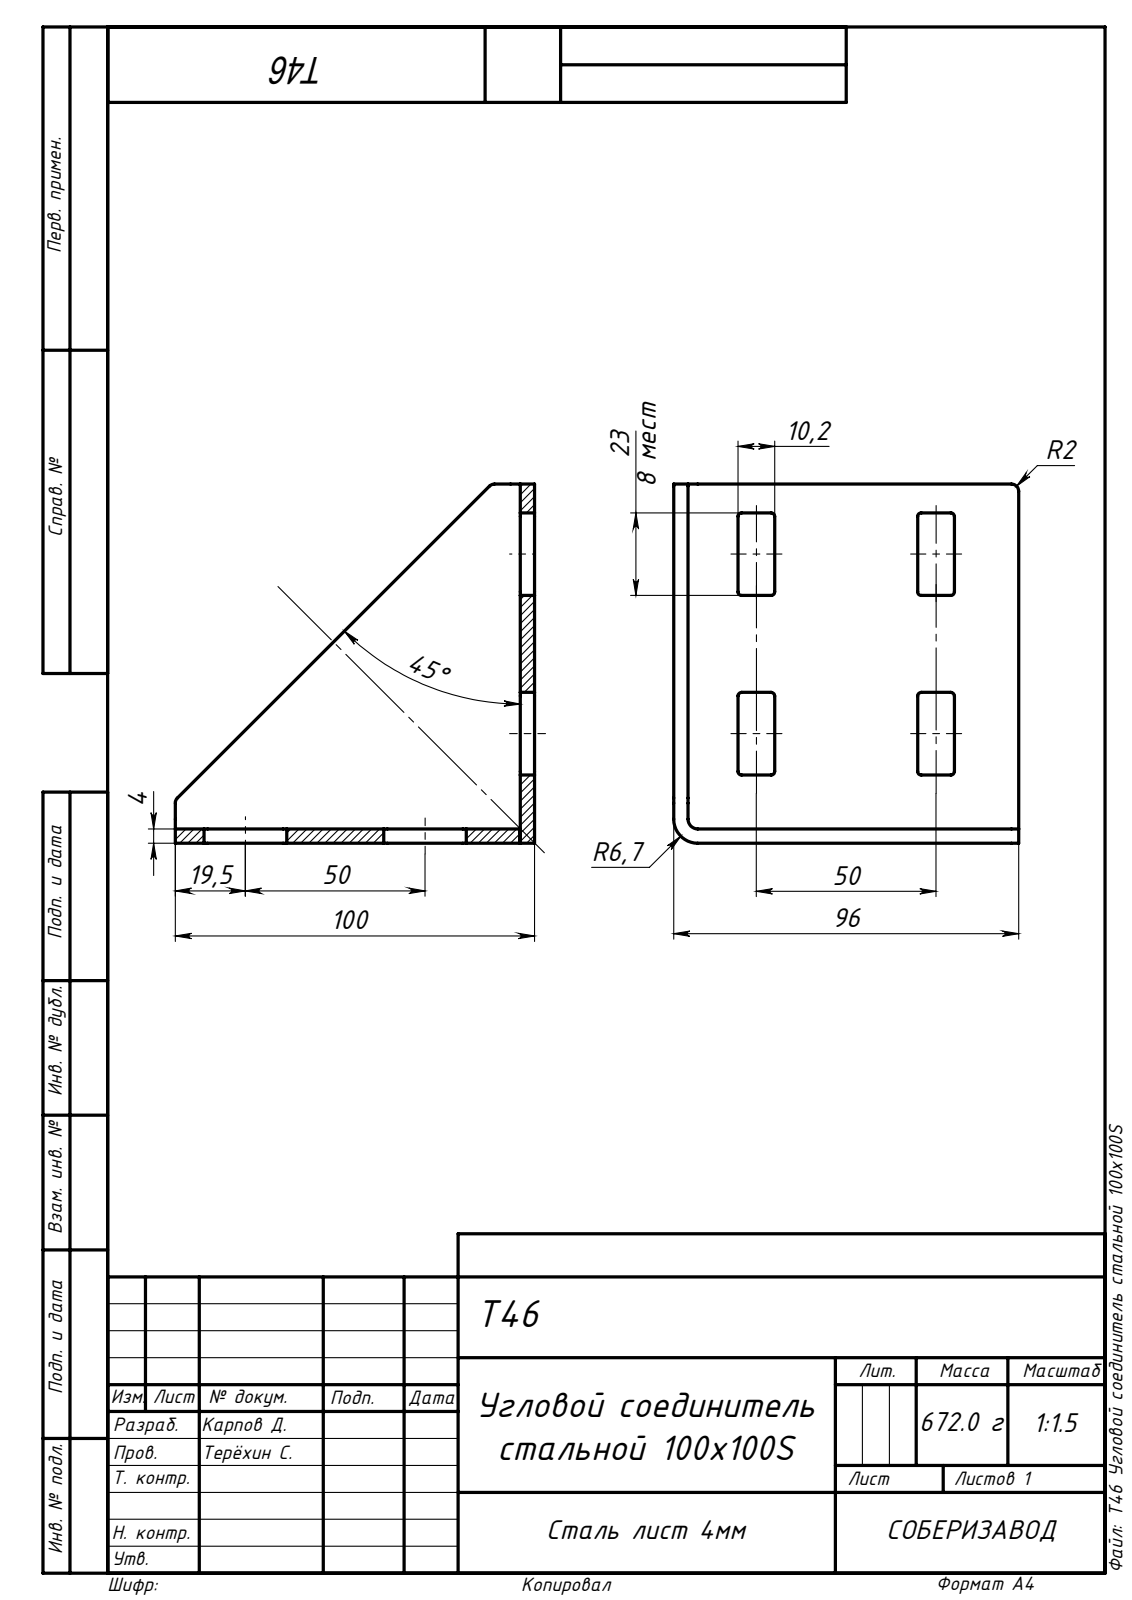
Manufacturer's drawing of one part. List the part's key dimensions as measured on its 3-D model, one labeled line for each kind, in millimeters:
STEP written by: SolidWorks 2021 (AUTOMOTIVE_DESIGN)
Units: millimetres
Bodies: 1 solid, 95 faces (53 planar, 42 cylindrical, 0 other)
Overall size (bounding box): 100 × 100 × 96
Volume: 87 323 mm³ · Surface area: 48 625 mm²
Partial cylindrical surfaces — rounded edges, fillets, slot ends (radius × count): R1 ×32, R2 ×6, R2.7 ×2, R6.7 ×2
Main face-to-face distances: 4, 96, 50, 92, 100, 17.9, 28.1, 67.9, 78.1, 10.2
